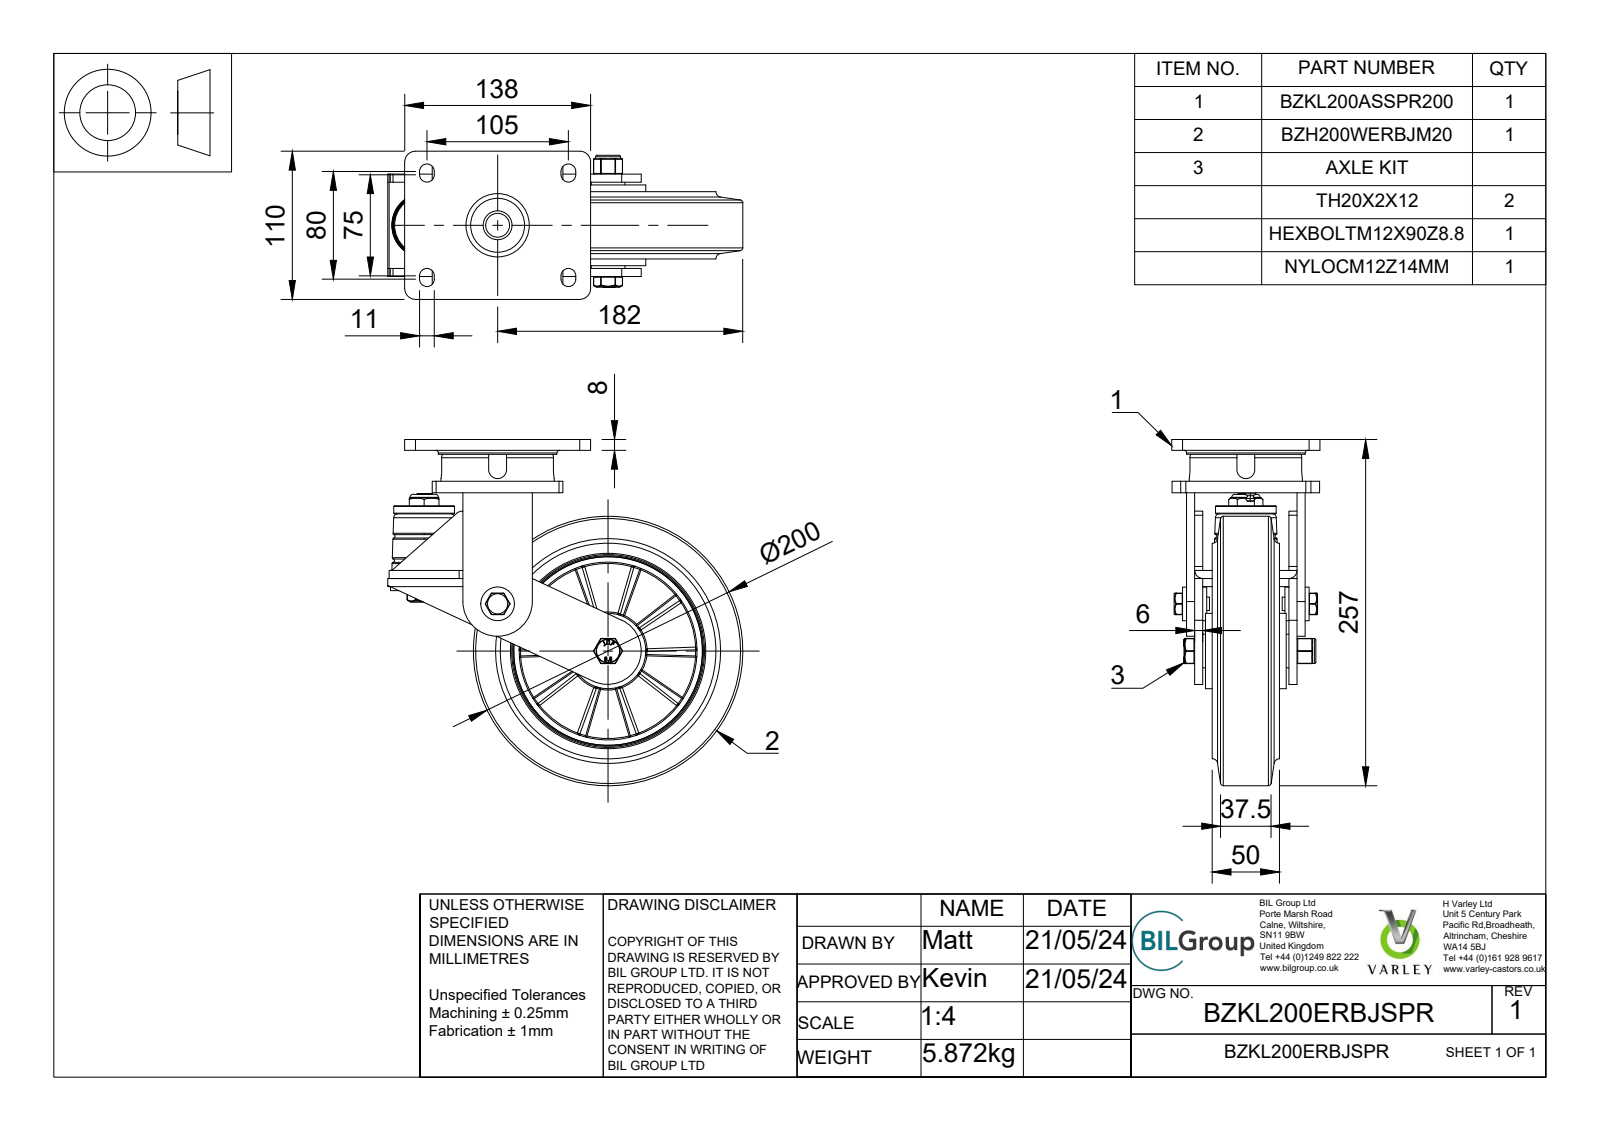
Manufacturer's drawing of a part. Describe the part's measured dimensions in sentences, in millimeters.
The part is named "BZKL200ERBJSPR v3; BZKL200ASSPR200 v1; FABRICATED STEEL TOP PLATE; FABRICATED STEEL FORKS (+6 more)". Its 3-D file was written by "Autodesk Translation Framework v13.14.0.145 (AUTOMOTIVE_DESIGN)". It is 50 solids with 1556 faces: 538 planar, 305 cylindrical and 713 other. Overall it measures 263.51 by 257 by 110 millimeters. Its volume is 1 576 000 cubic millimeters and its surface area 421 987 square millimeters. Round holes: 2 of diameter 12, 2 of diameter 47, 1 of diameter 10, 1 of diameter 12.1, 1 of diameter 12.2, 1 of diameter 14, 1 of diameter 20, 1 of diameter 28.5, 1 of diameter 30.8, 1 of diameter 40.3, 1 of diameter 40.5, 1 of diameter 42. Round bosses or shafts: 2 of diameter 25, 1 of diameter 200, 1 of diameter 141.5, 1 of diameter 88, 1 of diameter 84, 1 of diameter 56, 1 of diameter 50, 1 of diameter 45. Partial cylindrical surfaces (rounded edges, fillets, slot ends): 36 of radius 0.5, 8 of radius 5.5, 5 of radius 6, 4 of radius 0.47, 4 of radius 0.9, 4 of radius 4, 4 of radius 8, 3 of radius 3. The main face-to-face distances are 6, 76, 70, 7, 12, 8, 50, 23, 14, 57. The hole center spacings are 54.51, 89.16.
